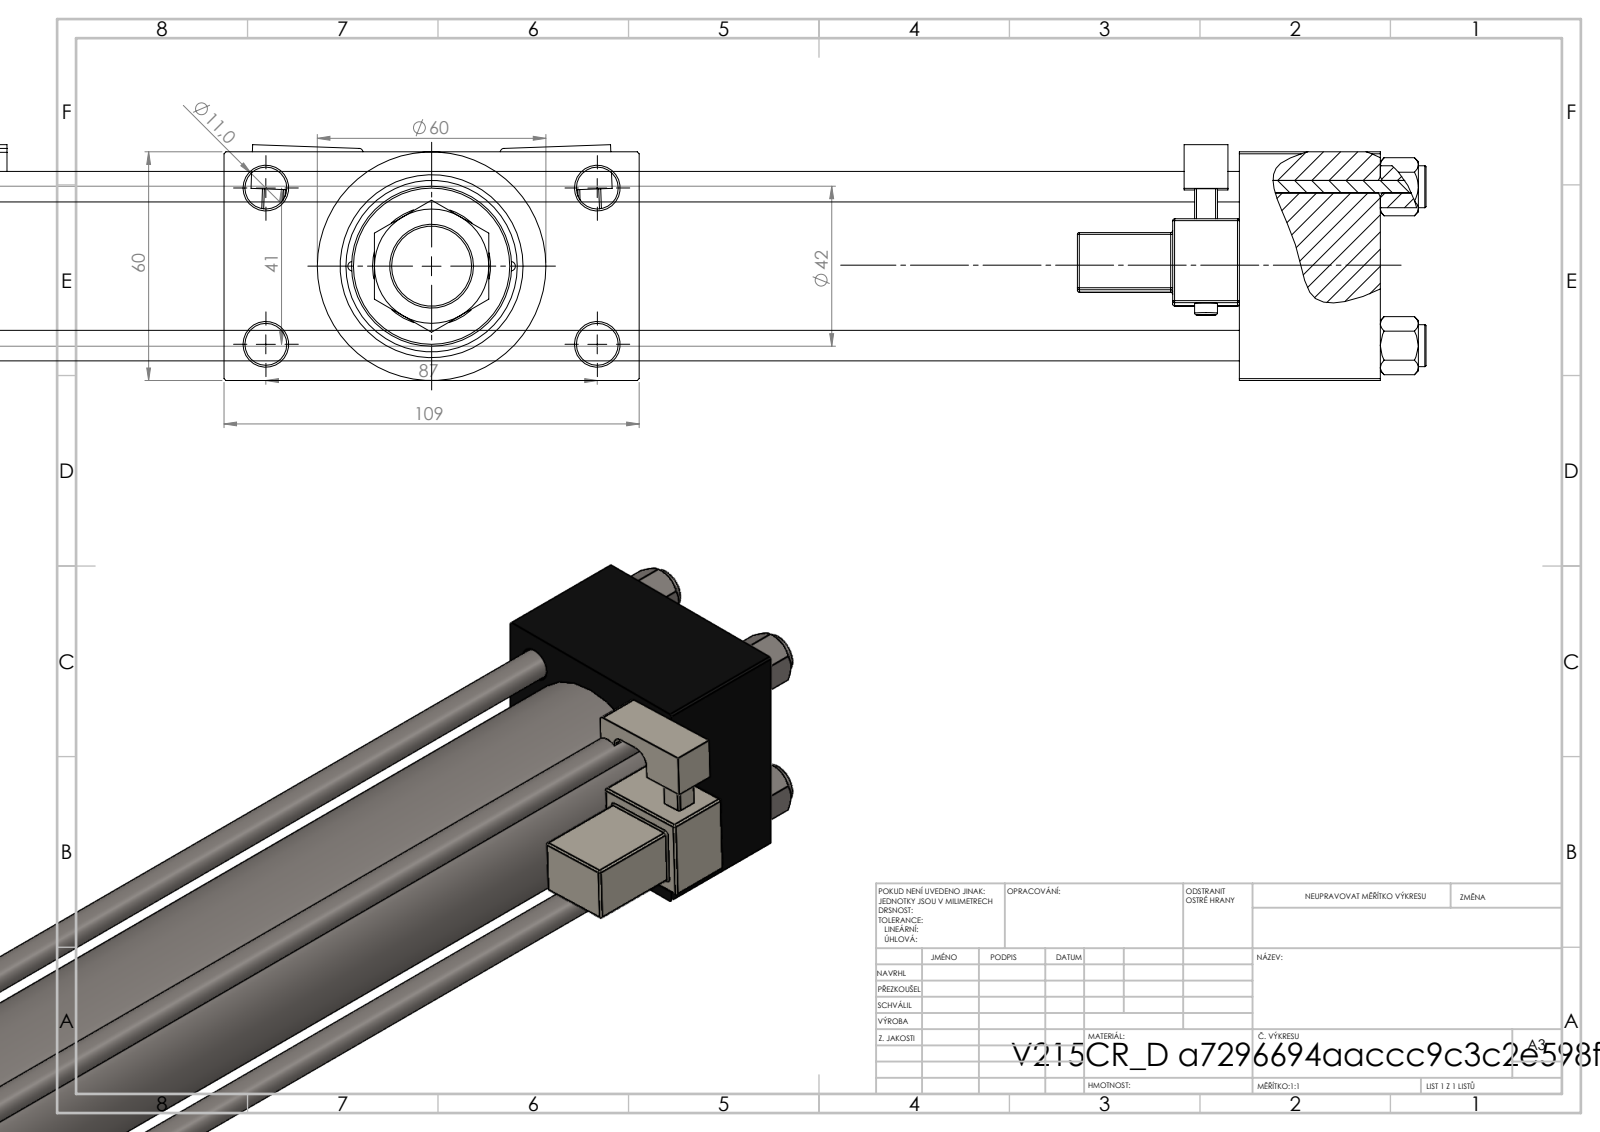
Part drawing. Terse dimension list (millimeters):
name: NUT_M5_D; MFA; V215CR_D_Body; V215CR_VCP_D (+3 more)
written by: SolidWorks 2019 (CONFIG_CONTROL_DESIGN)
unit: mm
bodies: 14 solids, 1320 faces (576 planar, 156 cylindrical, 588 other)
size: 510 × 109 × 61.9
volume: 936 318 mm³; area: 275 181 mm²
holes: 4× ⌀8, 4× ⌀11, 2× ⌀2.5, 2× ⌀7, 2× ⌀16.66, 2× ⌀24, 1× ⌀18.5, 1× ⌀28, 1× ⌀31, 1× ⌀40, 1× ⌀45
bosses: 4× ⌀11, 2× ⌀6, 1× ⌀60, 1× ⌀46, 1× ⌀42, 1× ⌀22, 1× ⌀14
rounds: 48× R0.5, 2× R1, 2× R2.5, 2× R4, 1× R13.5
face distances: 60, 338, 24.5, 84.5, 37, 375, 418, 381, 43, 109
hole spacings: 20.85, 22.65, 29.49, 30.62, 41.7, 46.53, 47.15, 48.09
